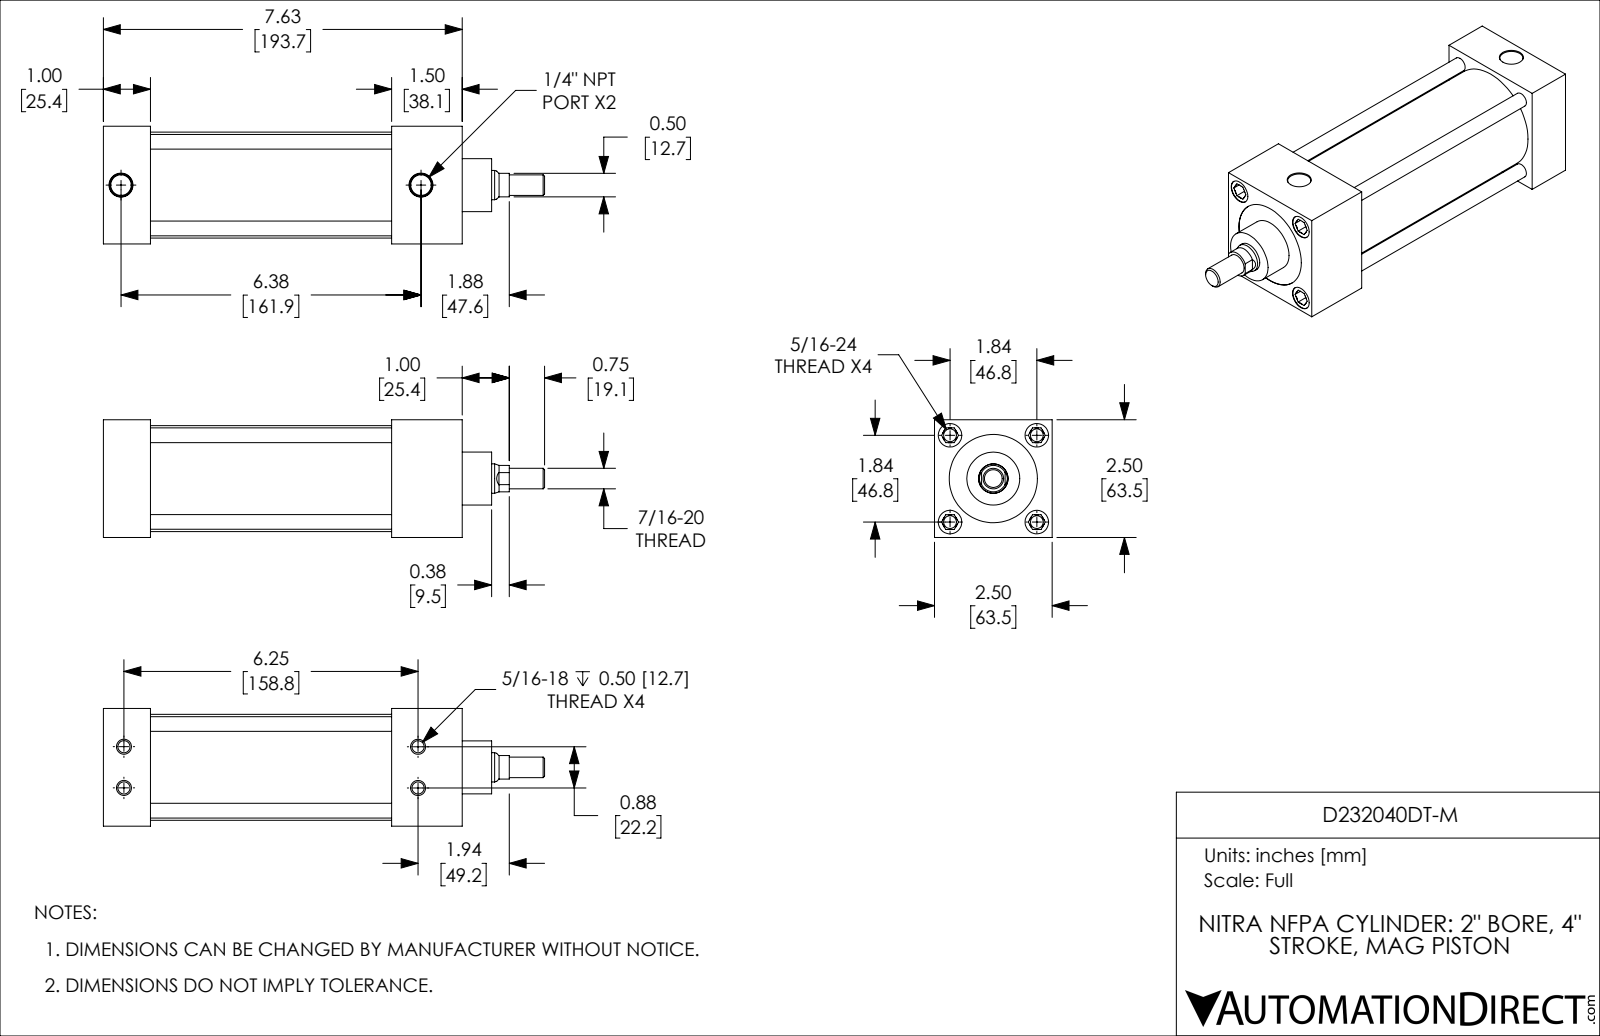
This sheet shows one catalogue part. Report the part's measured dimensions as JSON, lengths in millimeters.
{"part_name": "D232040DT-M_PISTON_KK1; D232040DT-M; D232040DT-M_BODY", "step_written_by": "SolidWorks 2019 (CONFIG_CONTROL_DESIGN)", "units": "millimeters", "bodies": {"solids": 2, "faces": 200, "planar": 58, "cylindrical": 62, "other": 80}, "overall_size": [238.1, 63.5, 63.5], "volume_mm3": 430000, "surface_area_mm2": 115400, "round_holes": [[6.9, 7], [6.5, 4], [12.7, 4], [11.1, 2], [15.9, 1], [47.6, 1], [50.8, 1]], "round_bosses_or_shafts": [[7.9, 4], [57.2, 1], [50.8, 1], [28.6, 1], [15.8, 1], [11.1, 1]], "partial_cylinders_radius": [[7.1, 1]], "face_to_face_distances": [63.5, 25.4, 155.6, 130.2, 28.6, 54, 101.6, 38.1, 193.7, 168.3], "hole_center_spacings": [46.7, 46.8, 33, 11.2, 11.3, 22.2, 33.1, 66.1]}
